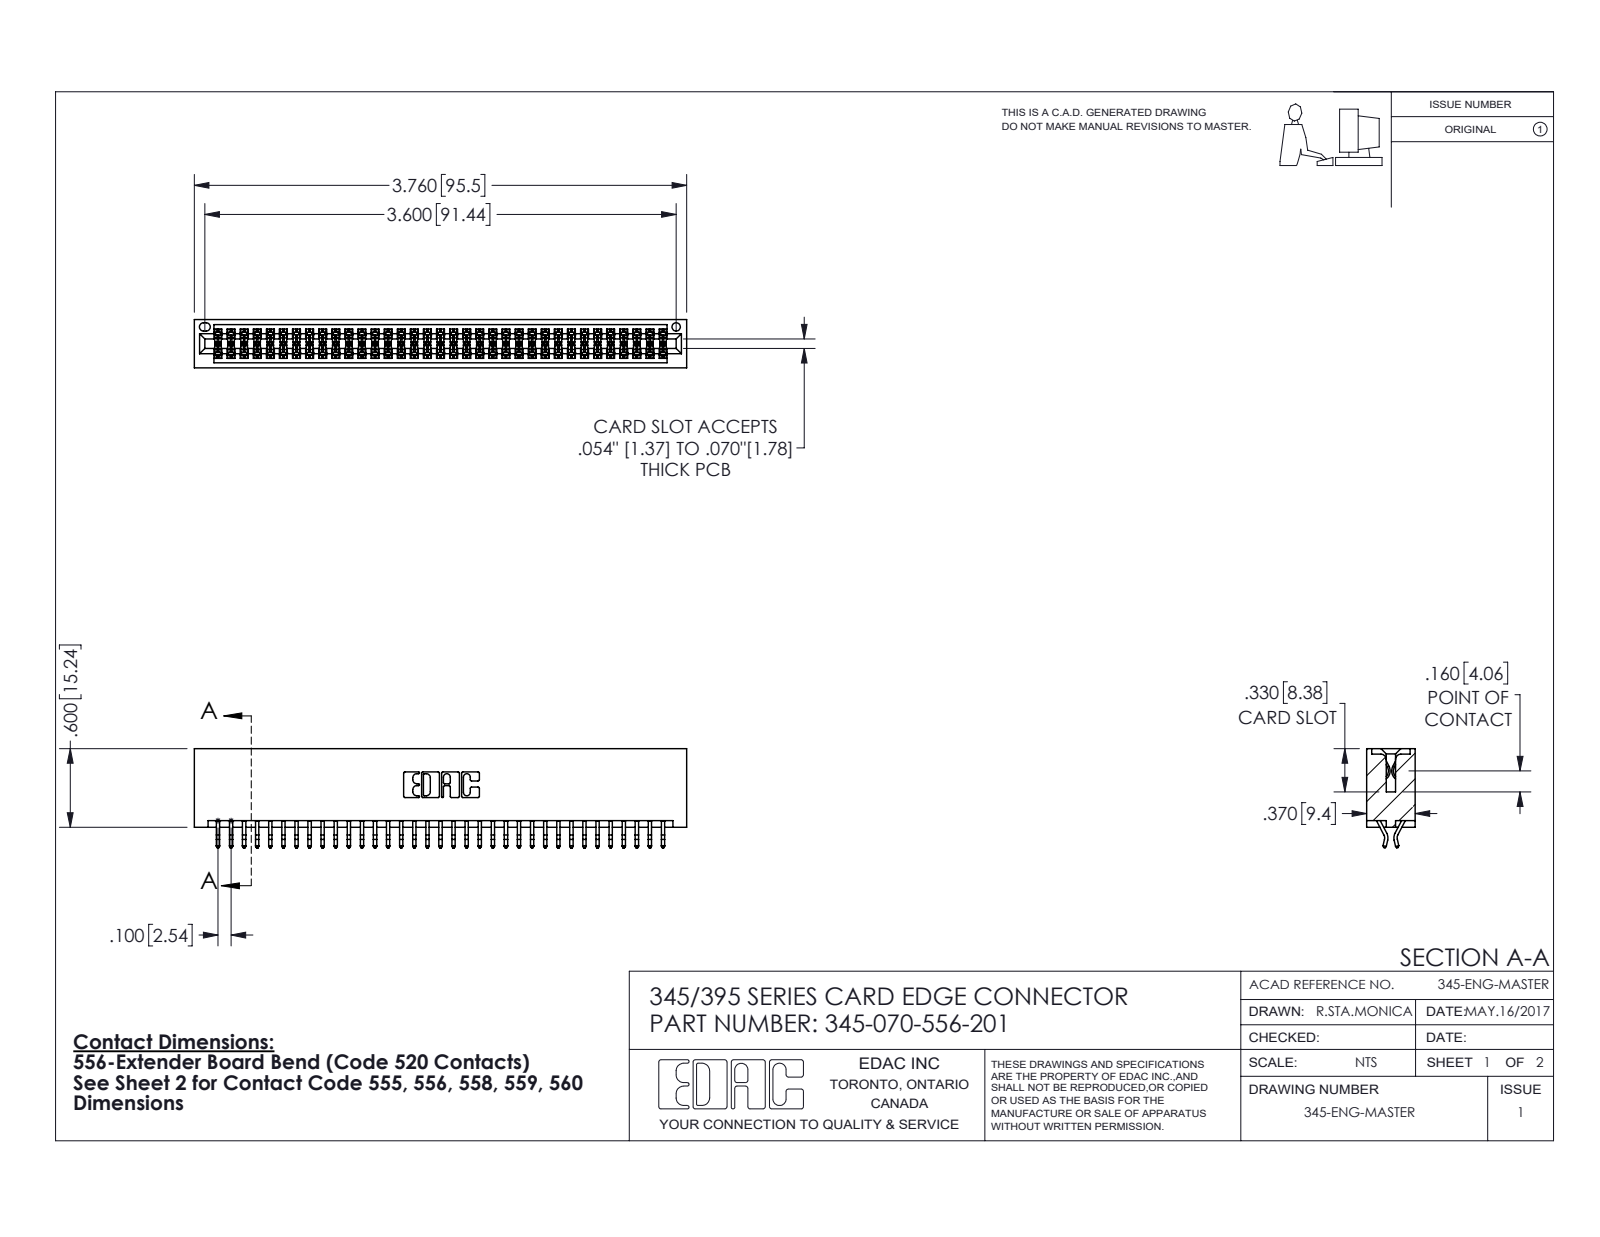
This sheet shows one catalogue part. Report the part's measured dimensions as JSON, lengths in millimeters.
{"part_name": "345-070-556-201; 345-292-001_556 Tail; 345 Part_No Mounting Lugs", "step_written_by": "SolidWorks 2016 (CONFIG_CONTROL_DESIGN)", "units": "millimeters", "bodies": {"solids": 71, "faces": 4038, "planar": 2666, "cylindrical": 1372, "other": 0}, "overall_size": [95.5, 19.2, 9.4], "volume_mm3": 9830, "surface_area_mm2": 14630, "round_holes": [[1.6, 1]], "partial_cylinders_radius": [[0.2, 105], [0.3, 22], [0.2, 6], [0.8, 6], [0.7, 3], [0.3, 2], [0.4, 2], [0.5, 2]], "face_to_face_distances": [7.6, 1.8, 5.1, 9.4, 0.6, 2.5, 6.9, 5.7, 4.4, 3.8]}
